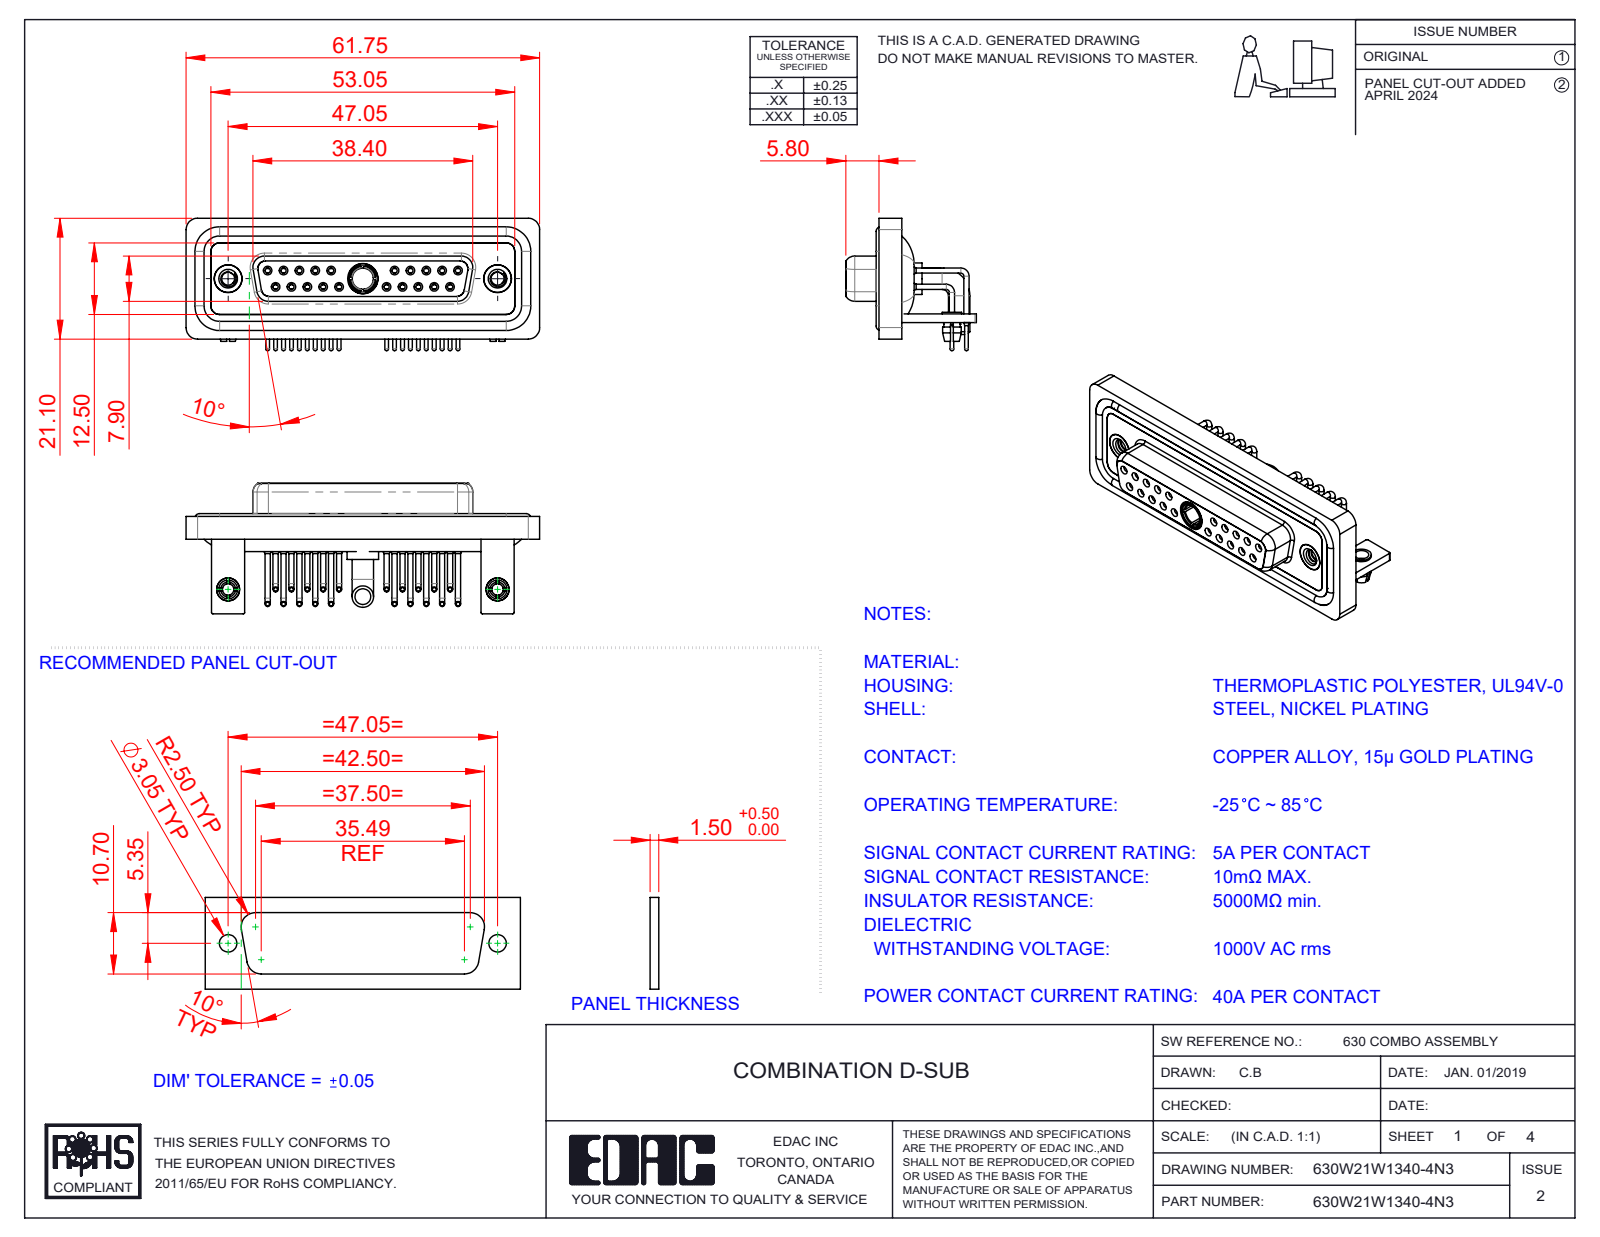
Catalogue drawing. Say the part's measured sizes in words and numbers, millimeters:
The part is named "630Combo Housing_21W1; 630Combo Board Lock_50 Contacts; 630Combo Waterproof Housing_25 Contacts; 630Combo Stabilizer Bracket_50 Contacts (+7 more)". Its 3-D file was written by "SolidWorks 2023 (CONFIG_CONTROL_DESIGN)". It is 33 solids with 1664 faces: 502 planar, 729 cylindrical and 433 other. Overall it measures 61.75 by 23.12 by 22.8 millimeters. Its volume is 8 981 cubic millimeters and its surface area 15 769 square millimeters. Round holes: 22 of diameter 2, 20 of diameter 0.9, 20 of diameter 1.1, 20 of diameter 1.5, 10 of diameter 1.6, 10 of diameter 1.7, 3 of diameter 4.85, 2 of diameter 2.26, 2 of diameter 2.5, 2 of diameter 3.2, 2 of diameter 4, 2 of diameter 4.05. Round bosses or shafts: 20 of diameter 0.9, 20 of diameter 0.65, 14 of diameter 1.6, 2 of diameter 4.95, 2 of diameter 4.8, 2 of diameter 4, 2 of diameter 3.75, 2 of diameter 3.4. Partial cylindrical surfaces (rounded edges, fillets, slot ends): 19 of radius 2, 18 of radius 1.5, 16 of radius 0.25, 8 of radius 1.35, 8 of radius 1.6, 5 of radius 0.5, 4 of radius 0.6, 4 of radius 0.65. The main face-to-face distances are 0.4, 1.8, 2.9, 3.7, 1.5, 4.1, 1.1, 1.4, 1.6, 2.5. The hole center spacings are 3.16, 2.77, 5.54, 8.31, 5.04, 19.39, 20.97, 22.16.
